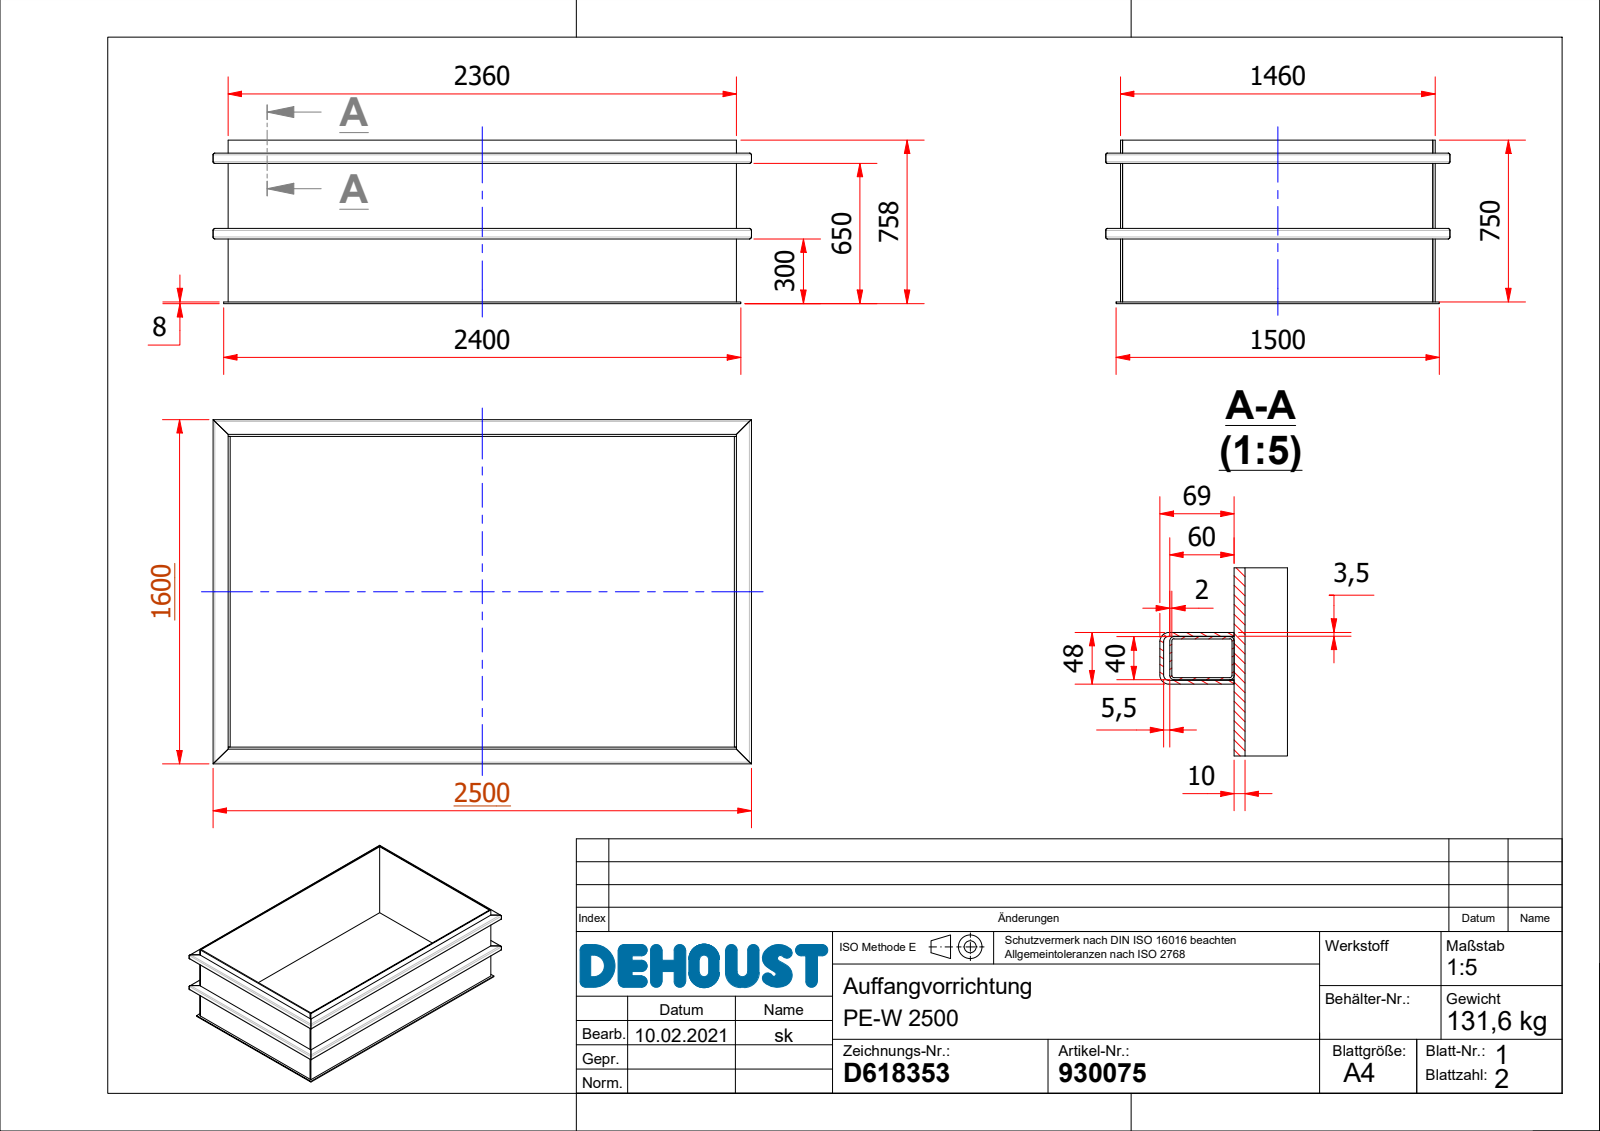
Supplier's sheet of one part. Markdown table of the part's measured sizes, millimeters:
| quantity | value |
| --- | --- |
| part name | D618353-0_-Auffangvorrichtung_2500; D618354-0_-Bodenplatte; D618355-0_-Längsseite; D618356-0_-Querseite (+4 more) |
| STEP written by | Autodesk Inventor 2019 (AUTOMOTIVE_DESIGN) |
| units | millimeters |
| bodies | 21 solids, 286 faces (190 planar, 96 cylindrical, 0 other) |
| overall size | 2498 × 1598 × 758 |
| volume | 101 400 000 mm³ |
| surface area | 30 410 000 mm² |
| partial cylindrical surfaces (radius × count) | 2 × 32, 4 × 32, 5 × 16, 8.5 × 16 |
| main face-to-face distances | 10, 8, 1450, 350, 2, 3.5, 2350, 1460, 44.5, 1440 |
